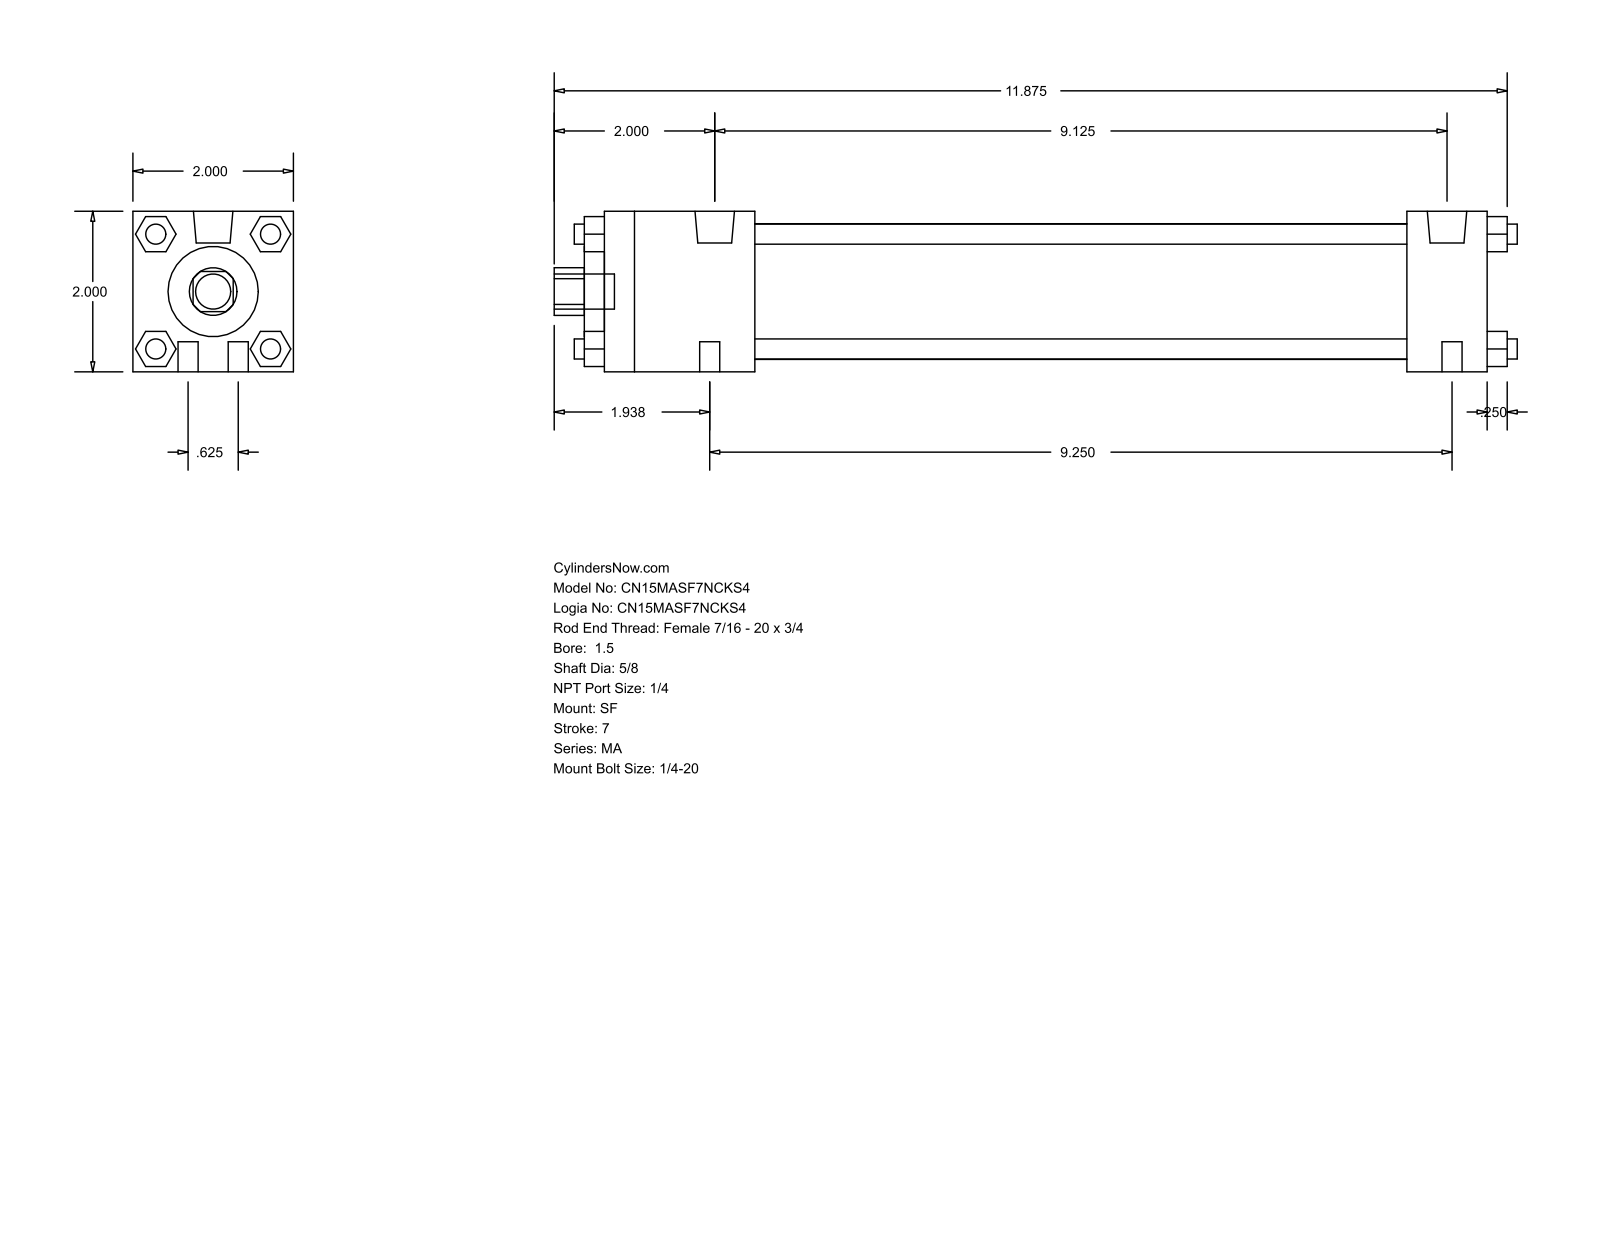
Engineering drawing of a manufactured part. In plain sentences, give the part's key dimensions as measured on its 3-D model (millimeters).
The part is named "MA_SF__0150_0.625". Its 3-D file was written by "GSSL Pune (CONFIG_CONTROL_DESIGN)". It is 0 solids with 124 faces: 94 planar, 30 cylindrical and 0 other. Overall it measures 304.8 by 50.8 by 50.8 millimeters. Round holes: 1 of diameter 15.88, 1 of diameter 28.57, 1 of diameter 42.93. Round bosses or shafts: 8 of diameter 6.35, 2 of diameter 12.49, 2 of diameter 7.94, 1 of diameter 11.11. Partial cylindrical surfaces (rounded edges, fillets, slot ends): 1 of radius 7.54. The main face-to-face distances are 50.8, 279.39, 6.35, 285.74, 47.62, 254, 206.38, 231.77, 25.39, 53.97.
